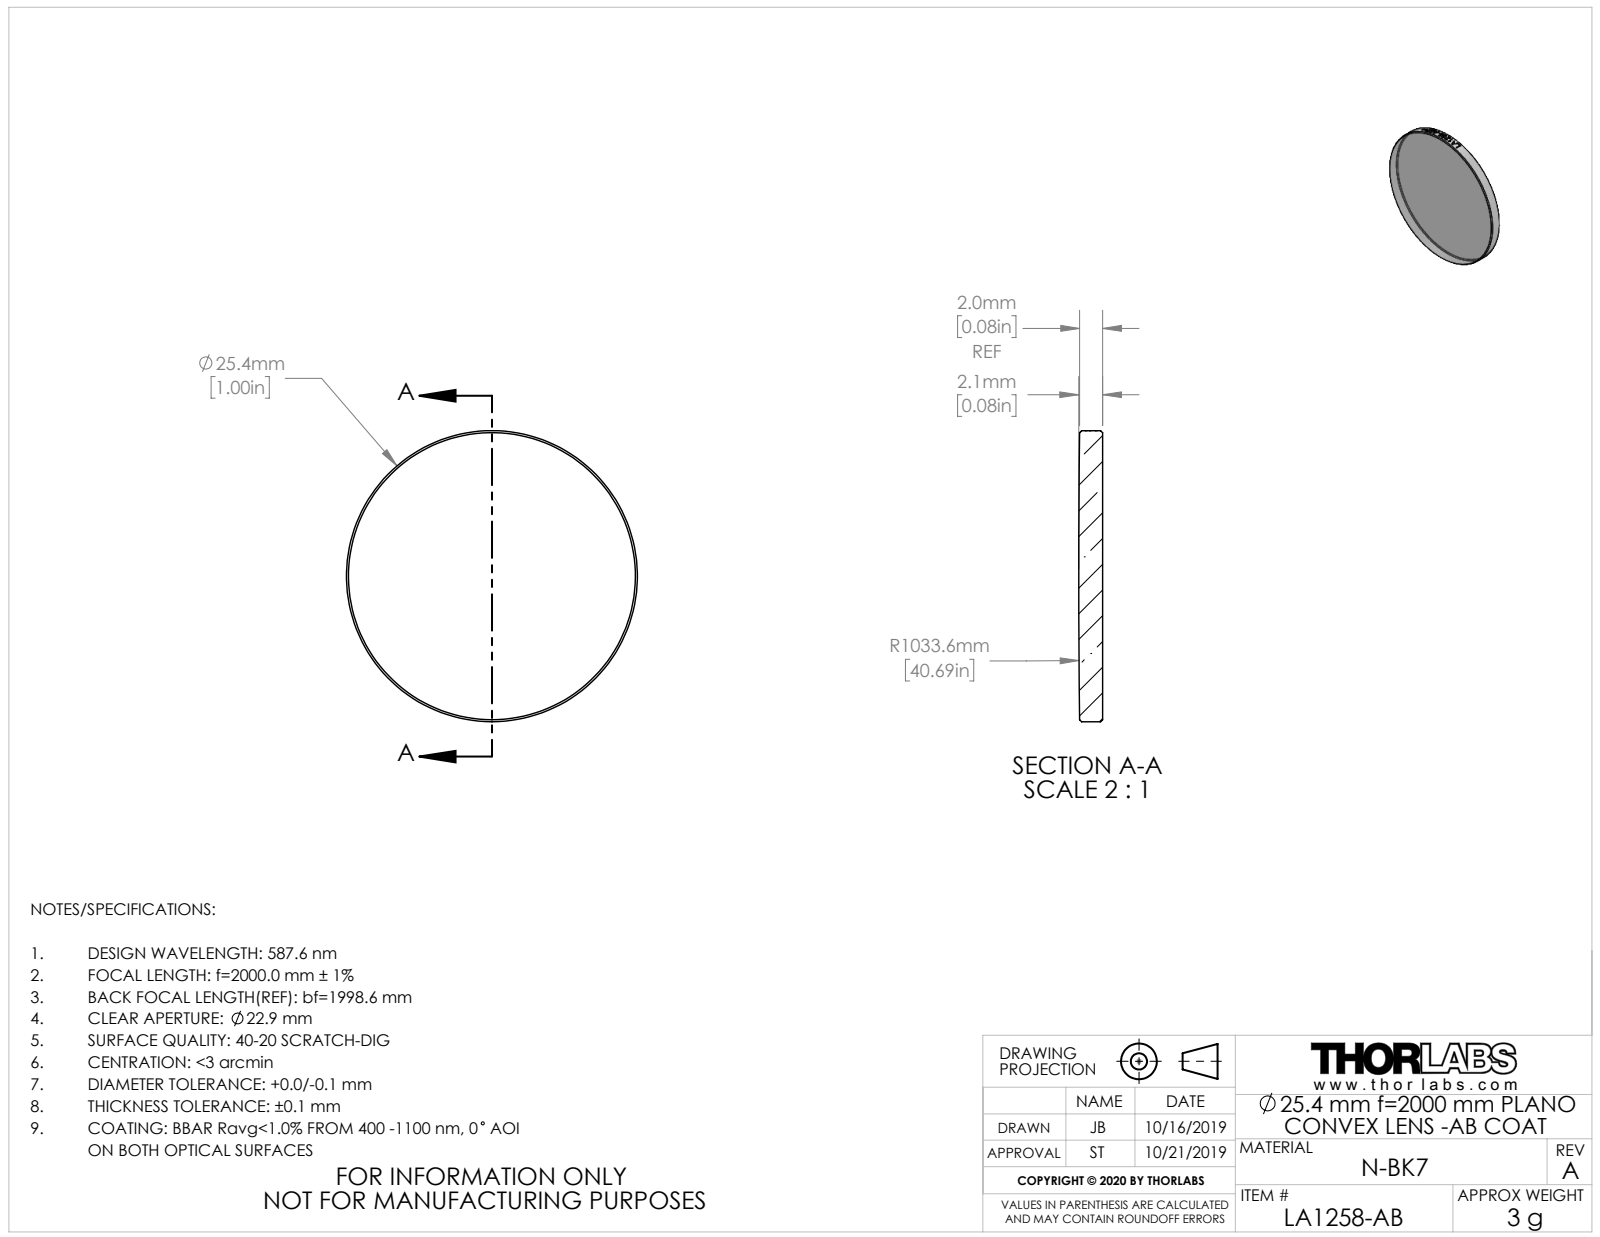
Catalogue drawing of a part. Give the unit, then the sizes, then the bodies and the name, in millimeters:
Units: millimetres
Overall size (bounding box): 25.4 × 25.4 × 2.1
Round bosses / shafts (diameter × count): ⌀25.4 ×1
Volume: 1 000 mm³ · Surface area: 1 157 mm²
Bodies: 1 solid, 30 faces (1 planar, 23 cylindrical, 6 other)
Part name (STEP PRODUCT): TTN195776-E0W
STEP written by: SolidWorks 2018 (CONFIG_CONTROL_DESIGN)
